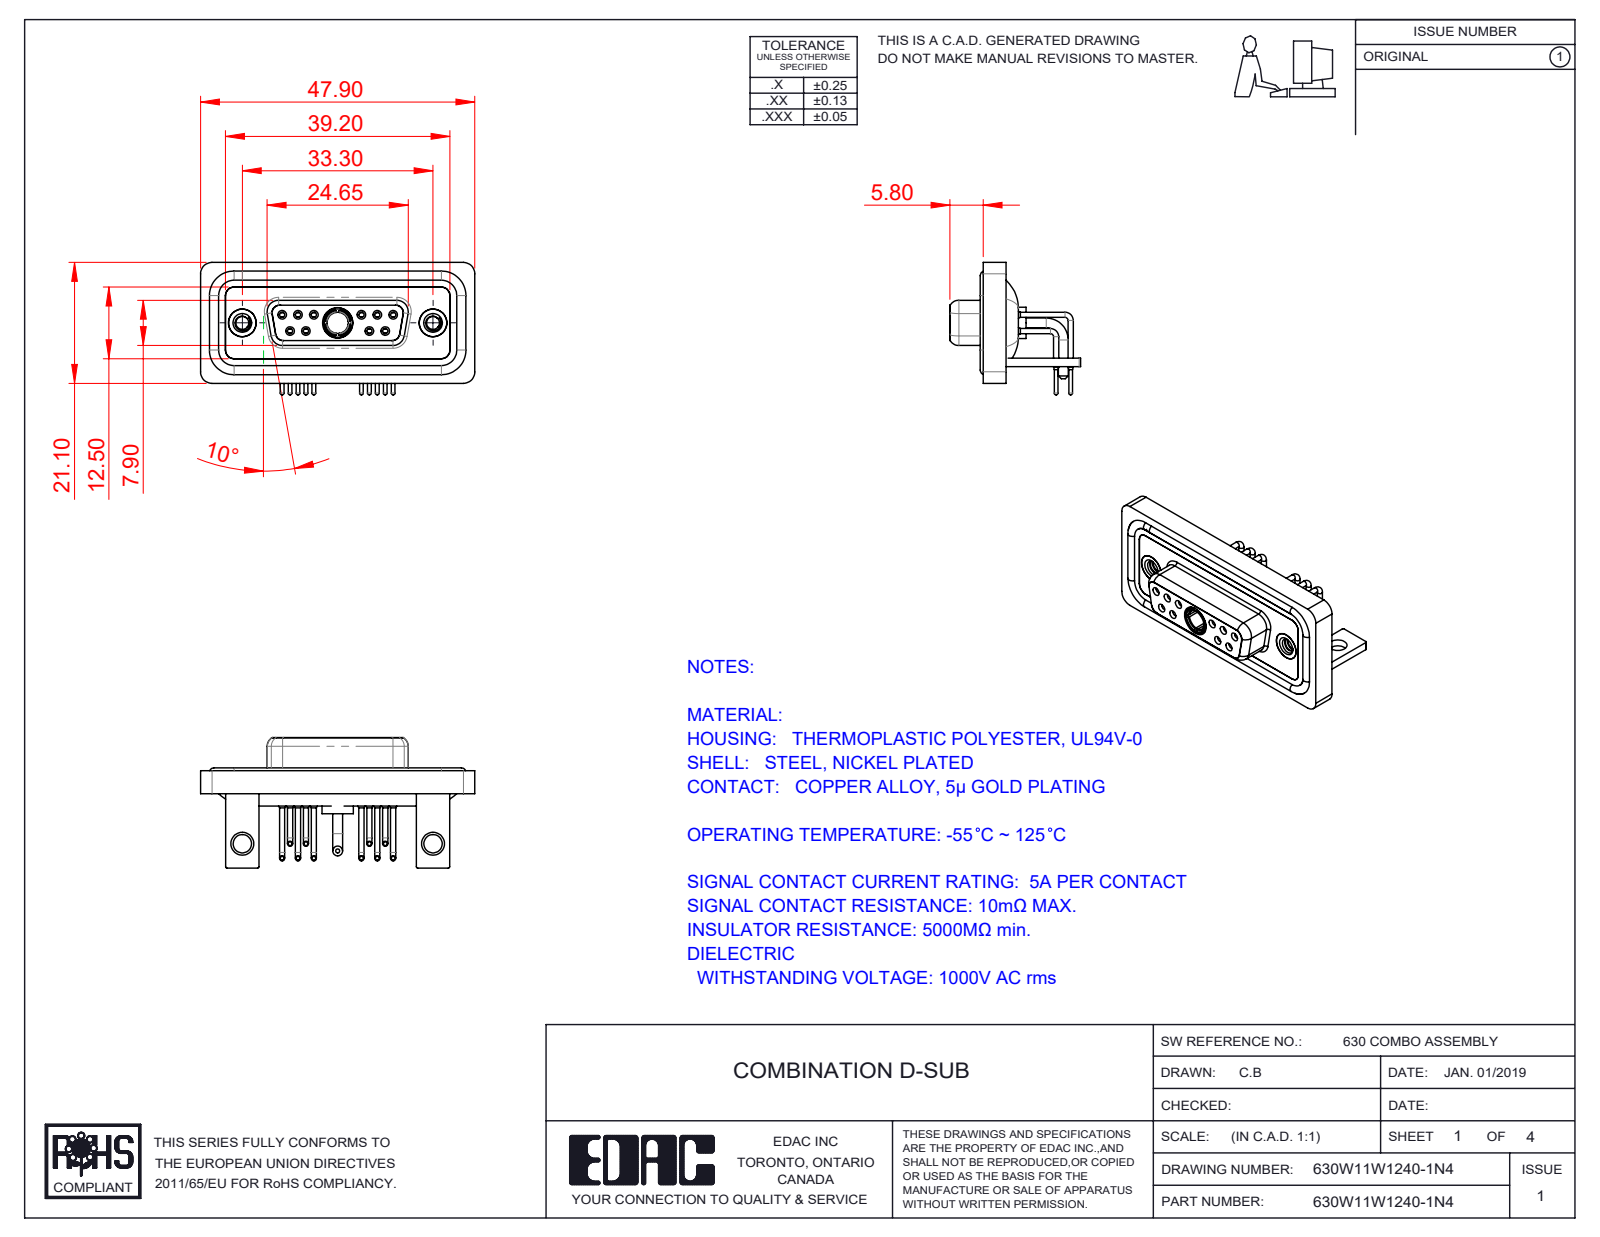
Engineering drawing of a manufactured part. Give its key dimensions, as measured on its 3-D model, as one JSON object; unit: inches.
{"part_name": "630Combo Waterproof Housing_15 Contacts; 630Combo Threaded Rivet_2; 630Combo Stabilizer Bracket_50 Contacts; 630Combo Contact Row 1_50 Contacts (+6 more)", "step_written_by": "SolidWorks 2020 (CONFIG_CONTROL_DESIGN)", "units": "inches", "bodies": {"solids": 21, "faces": 1042, "planar": 304, "cylindrical": 467, "other": 271}, "overall_size": [1.886, 0.91, 0.898], "volume_in3": 0.398, "surface_area_in2": 17.29, "round_holes": [[0.035, 10], [0.043, 10], [0.059, 10], [0.079, 10], [0.067, 6], [0.063, 4], [0.191, 3], [0.089, 2], [0.126, 2], [0.157, 2], [0.159, 2], [0.197, 2]], "round_bosses_or_shafts": [[0.063, 10], [0.035, 10], [0.026, 10], [0.195, 2], [0.189, 2], [0.067, 2], [0.217, 1], [0.205, 1]], "partial_cylinders_radius": [[0.079, 21], [0.059, 18], [0.01, 16], [0.053, 12], [0.063, 8], [0.02, 5], [0.024, 4], [0.026, 4]], "face_to_face_distances": [0.016, 0.114, 0.071, 0.059, 0.146, 0.043, 0.063, 0.161, 0.031, 0.098], "hole_center_spacings": [0.124, 0.109, 0.545, 0.436, 0.654, 0.198, 0.198, 0.218]}
